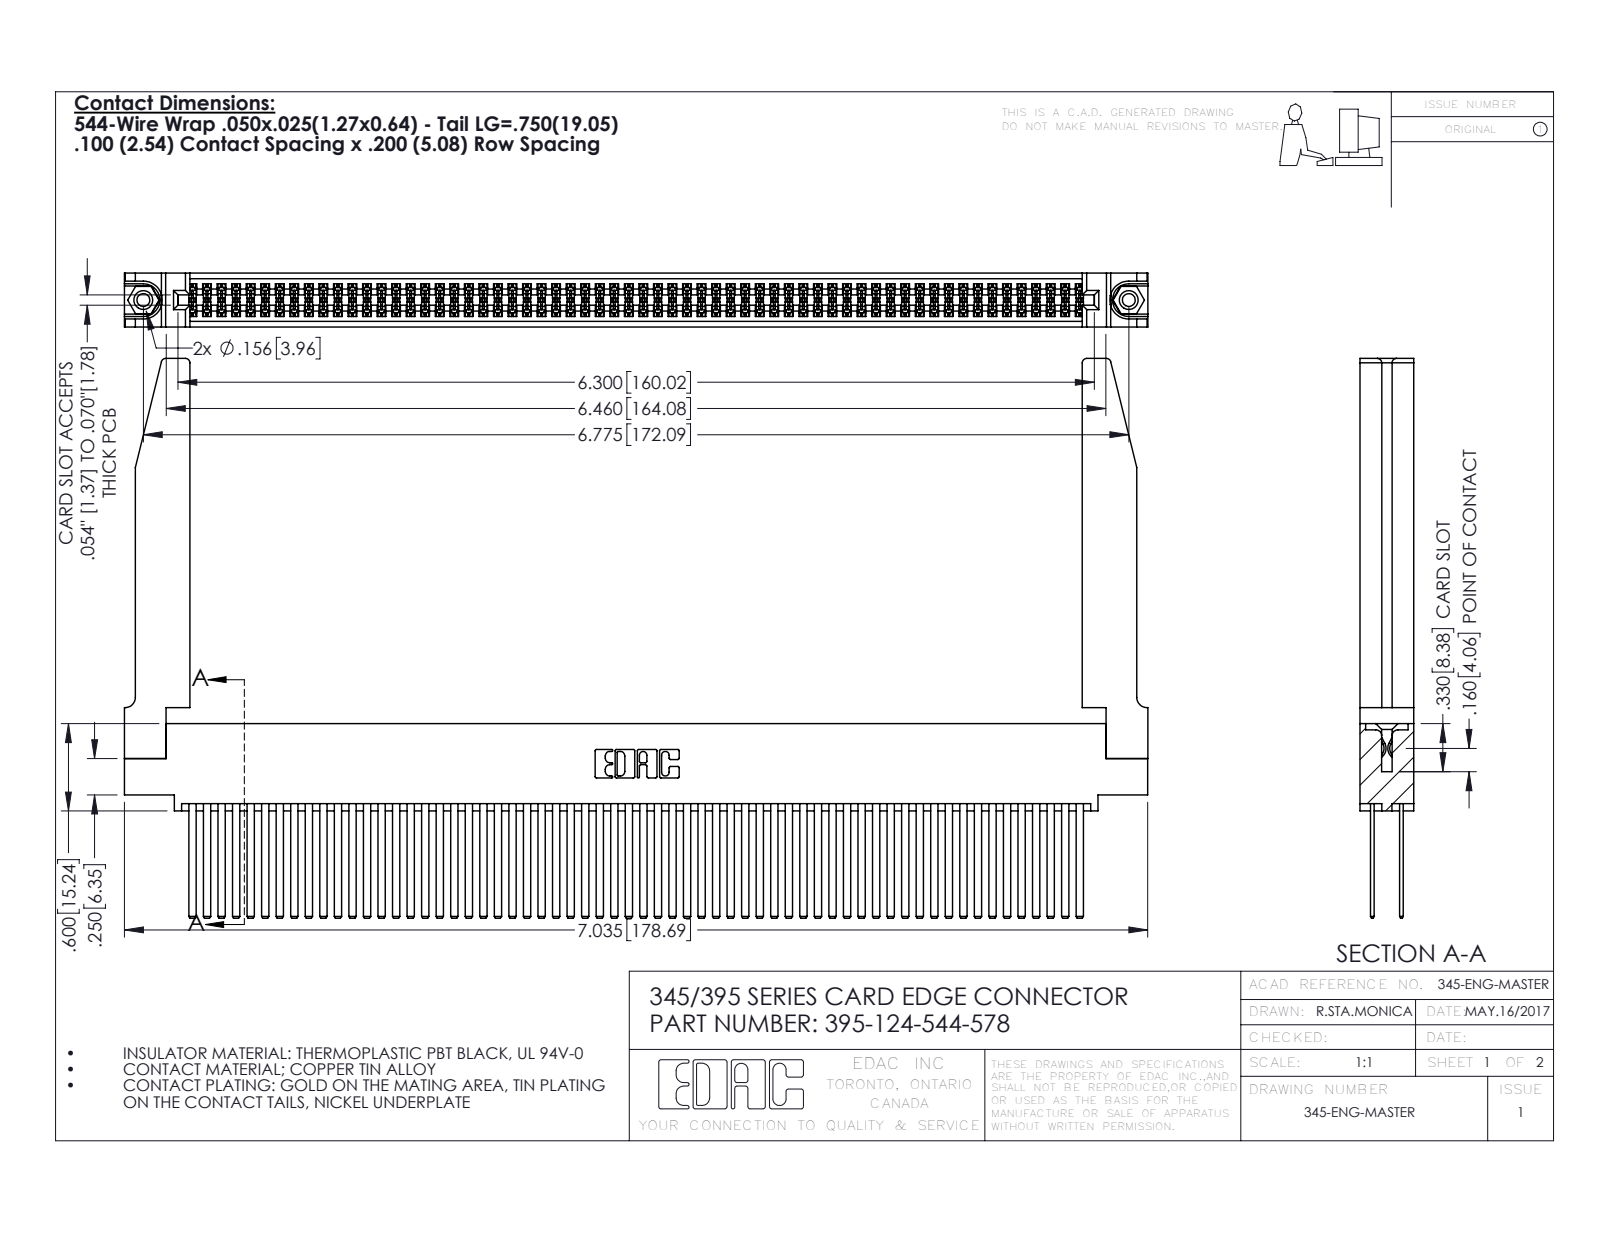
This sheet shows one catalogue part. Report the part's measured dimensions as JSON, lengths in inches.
{"part_name": "345-250-001_345-250-001-102; 345-292-001_345-293-144; 345-220-078_345-220-078; 345 Part_0.110 Offset - 0.156 Dia-TH (+1 more)", "step_written_by": "SolidWorks 2016 (CONFIG_CONTROL_DESIGN)", "units": "inches", "bodies": {"solids": 129, "faces": 5820, "planar": 3822, "cylindrical": 1946, "other": 52}, "overall_size": [7.036, 3.847, 0.37], "volume_in3": 1.647, "surface_area_in2": 63.26, "round_holes": [[0.089, 2], [0.125, 2], [0.156, 2], [0.064, 1]], "round_bosses_or_shafts": [[0.155, 2]], "partial_cylinders_radius": [[0.006, 186], [0.01, 22], [0.03, 8], [0.007, 6], [0.031, 6], [0.026, 3], [0.014, 2], [0.019, 2]], "face_to_face_distances": [0.072, 0.298, 0.098, 0.272, 0.025, 0.2, 0.37, 0.225, 0.175, 0.148], "hole_center_spacings": [0.27, 6.539, 6.775]}
